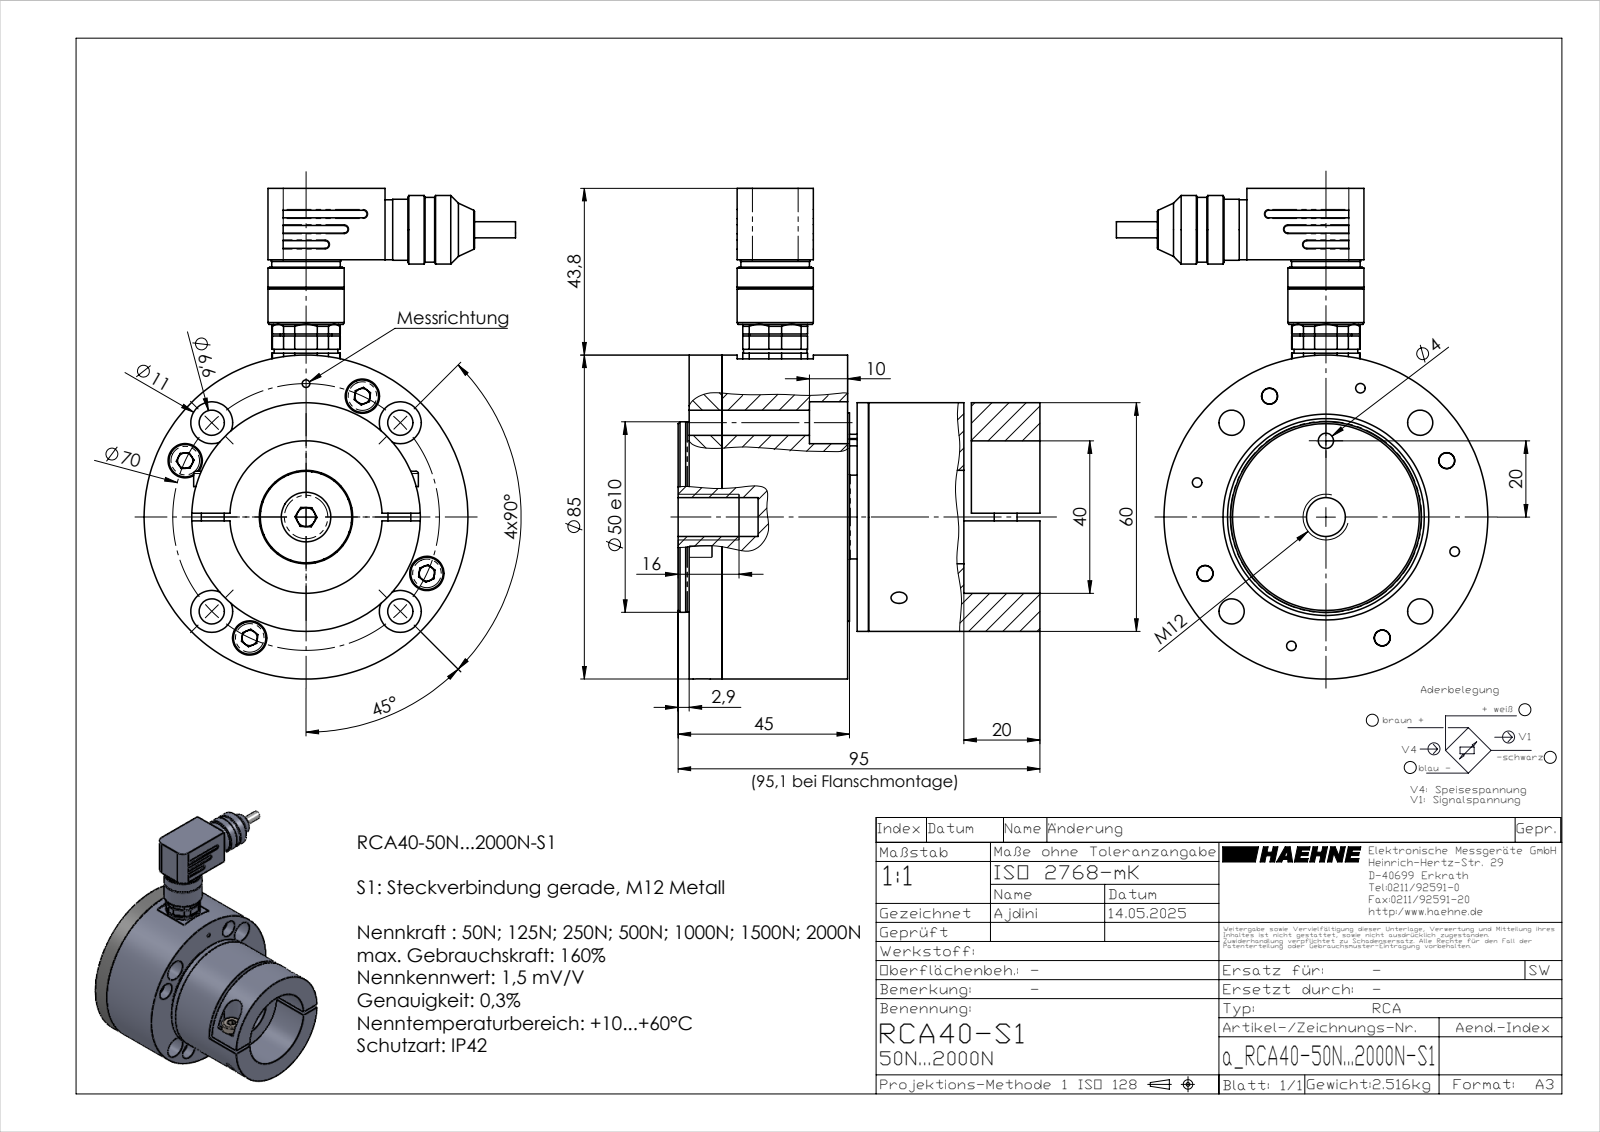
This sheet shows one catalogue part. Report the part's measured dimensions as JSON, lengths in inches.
{"part_name": "inafag_1203-tvh_7zkvytp7yxkimpdvw8sj0b5w4_11; inafag_1203-tvh_7zkvytp7yxkimpdvw8sj0b5w4_15; inafag_1203-tvh_7zkvytp7yxkimpdvw8sj0b5w4_18; inafag_1203-tvh_7zkvytp7yxkimpdvw8sj0b5w4_21 (+8 more)", "step_written_by": "SolidWorks 2023 (AUTOMOTIVE_DESIGN)", "units": "inches", "bodies": {"solids": 55, "faces": 808, "planar": 408, "cylindrical": 228, "other": 172}, "overall_size": [5.069, 3.838, 3.744], "volume_in3": 22.38, "surface_area_in2": 179.9, "round_holes": [[0.134, 9], [0.098, 8], [0.26, 6], [0.165, 5], [0.157, 4], [0.209, 4], [0.354, 4], [0.433, 4], [0.177, 2], [0.197, 2], [0.079, 1], [0.236, 1]], "round_bosses_or_shafts": [[0.118, 9], [0.224, 8], [0.335, 4], [0.197, 4], [0.059, 4], [0.039, 4], [0.709, 2], [0.669, 2]], "partial_cylinders_radius": [[0.008, 12], [0.039, 11], [0.012, 6], [0.157, 2], [0.217, 2], [0.022, 1], [0.026, 1], [0.03, 1]], "face_to_face_distances": [0.118, 0.079, 0.339, 1.854, 1.398, 0.457, 1.181, 0.787, 1.772, 1.972], "hole_center_spacings": [1.378, 1.949, 0.976, 0.992, 1.291, 2.013, 2.223, 0.236]}
